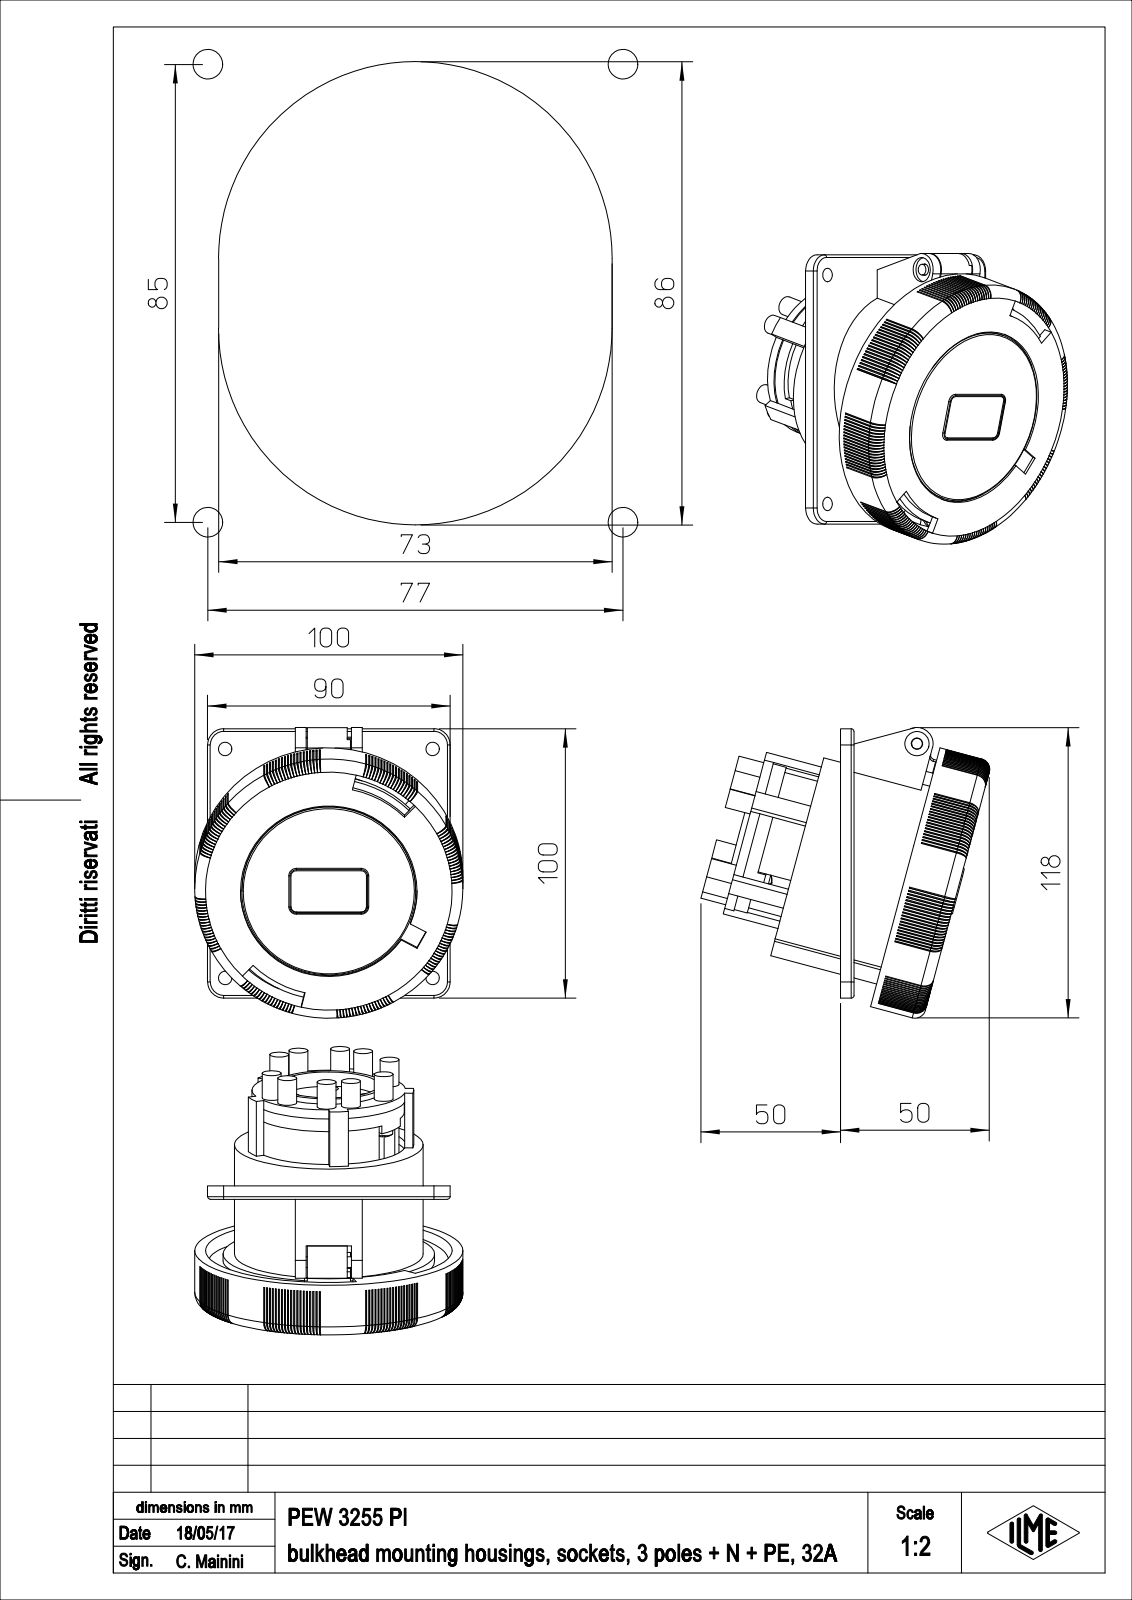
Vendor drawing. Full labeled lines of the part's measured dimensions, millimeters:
Part name (STEP PRODUCT): PEW_3255_PI
STEP written by: PTC Creo Elements/Direct Modeling 19.0E 27-Jun-2016 (C) Parametric Technology GmbH (AUTOMOTIVE_DESIGN)
Units: millimetres
Bodies: 1 solid, 1440 faces (642 planar, 307 cylindrical, 491 other)
Overall size (bounding box): 107.91 × 107.09 × 99.5
Volume: 269 783 mm³ · Surface area: 105 069 mm²
Round holes (diameter × count): ⌀7 ×5, ⌀5 ×4, ⌀7.5 ×4, ⌀14 ×4, ⌀4.2 ×1, ⌀9 ×1, ⌀9.5 ×1, ⌀37 ×1, ⌀57 ×1, ⌀58.5 ×1, ⌀61.7 ×1, ⌀65.3 ×1
Round bosses / shafts (diameter × count): ⌀7 ×11, ⌀6.7 ×2, ⌀99.5 ×1, ⌀85 ×1, ⌀78.5 ×1, ⌀75.5 ×1, ⌀70 ×1, ⌀64.5 ×1
Partial cylindrical surfaces — rounded edges, fillets, slot ends (radius × count): R3.6 ×152, R6 ×6, R0.4 ×4, R1 ×4, R2 ×4, R0.2 ×3, R4 ×2, R26 ×2
Main face-to-face distances: 5, 3, 57.7, 2, 20, 17, 60.7, 40.7, 6.7, 11.19
Hole centre spacings: 28.81, 17.81, 15.15, 15.14, 15.16, 28.82, 17.8, 15.12
